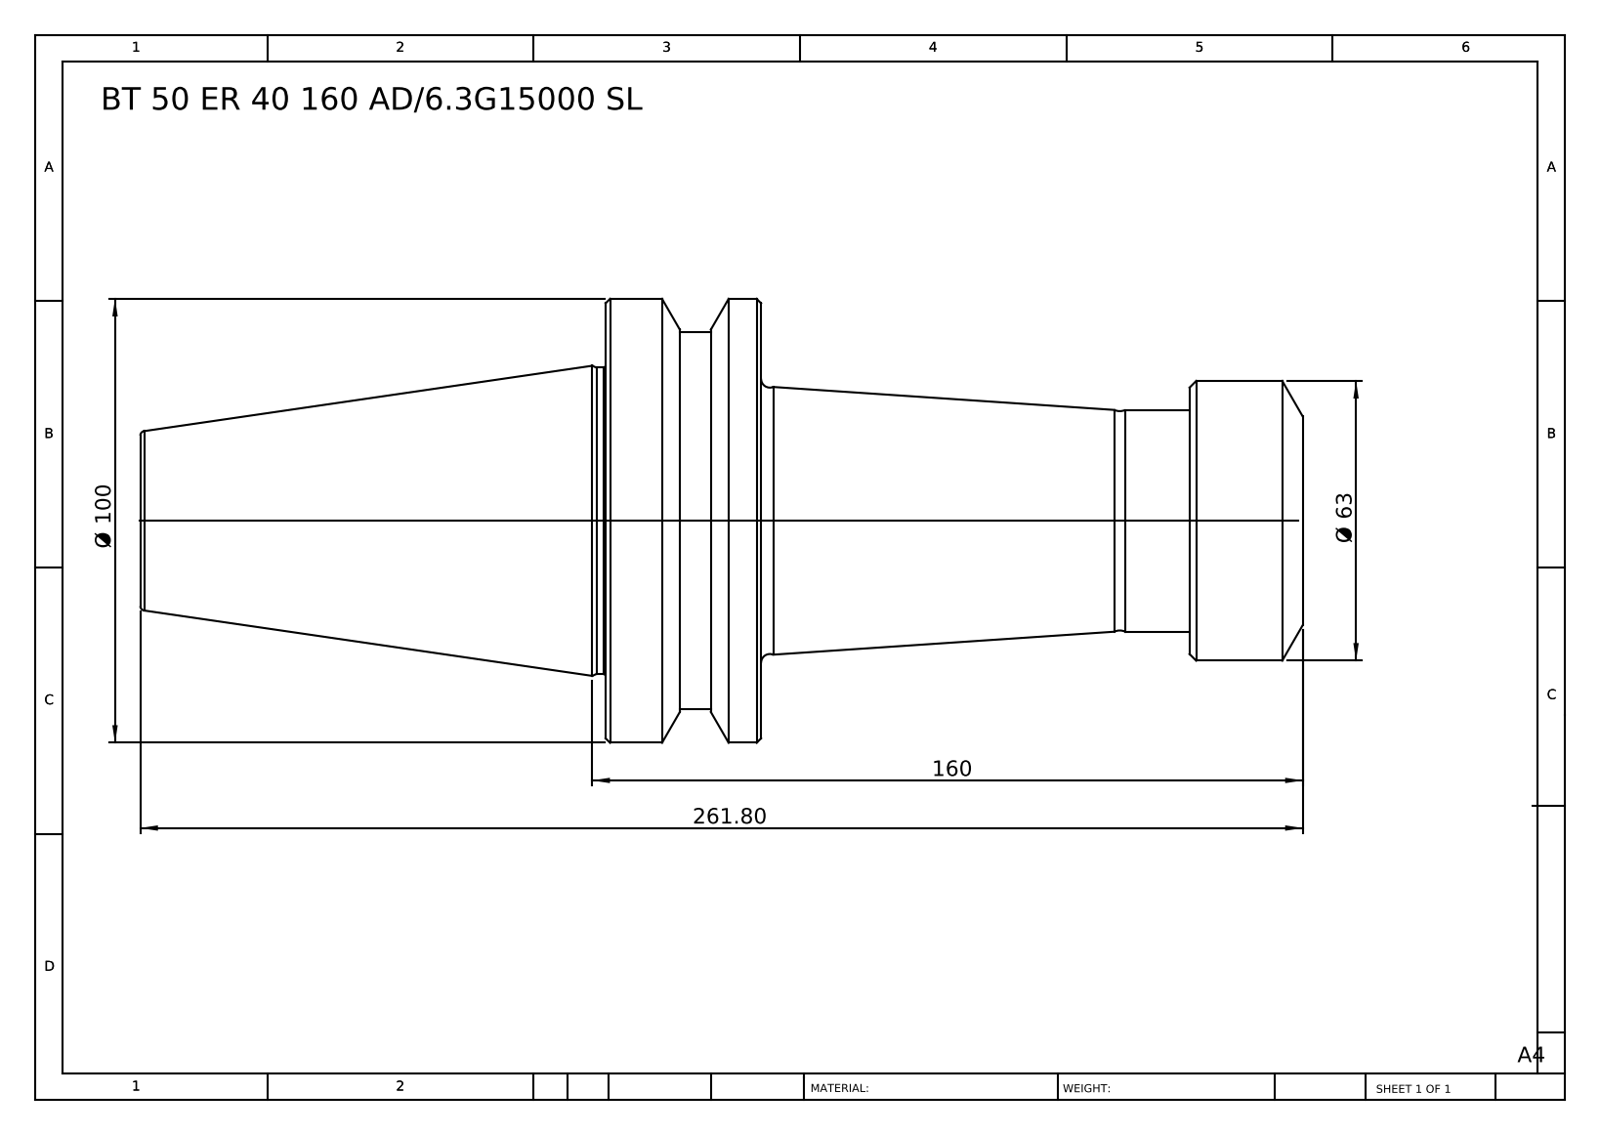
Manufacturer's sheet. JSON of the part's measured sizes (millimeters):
{"part_name": "BT 50 ER 40 160 AD-6.3G15000 SL", "step_written_by": "SolidWorks 2014 (CONFIG_CONTROL_DESIGN)", "units": "millimeters", "bodies": {"solids": 1, "faces": 49, "planar": 7, "cylindrical": 12, "other": 30}, "overall_size": [261.81, 100, 100], "volume_mm3": 810823, "surface_area_mm2": 66347, "round_bosses_or_shafts": [[100, 1], [85, 1], [69, 1], [63, 1], [49.9, 1]], "face_to_face_distances": [35, 122, 157, 261.8, 139.8, 104.8, 25.5, 96.5, 131.5, 236.3]}
